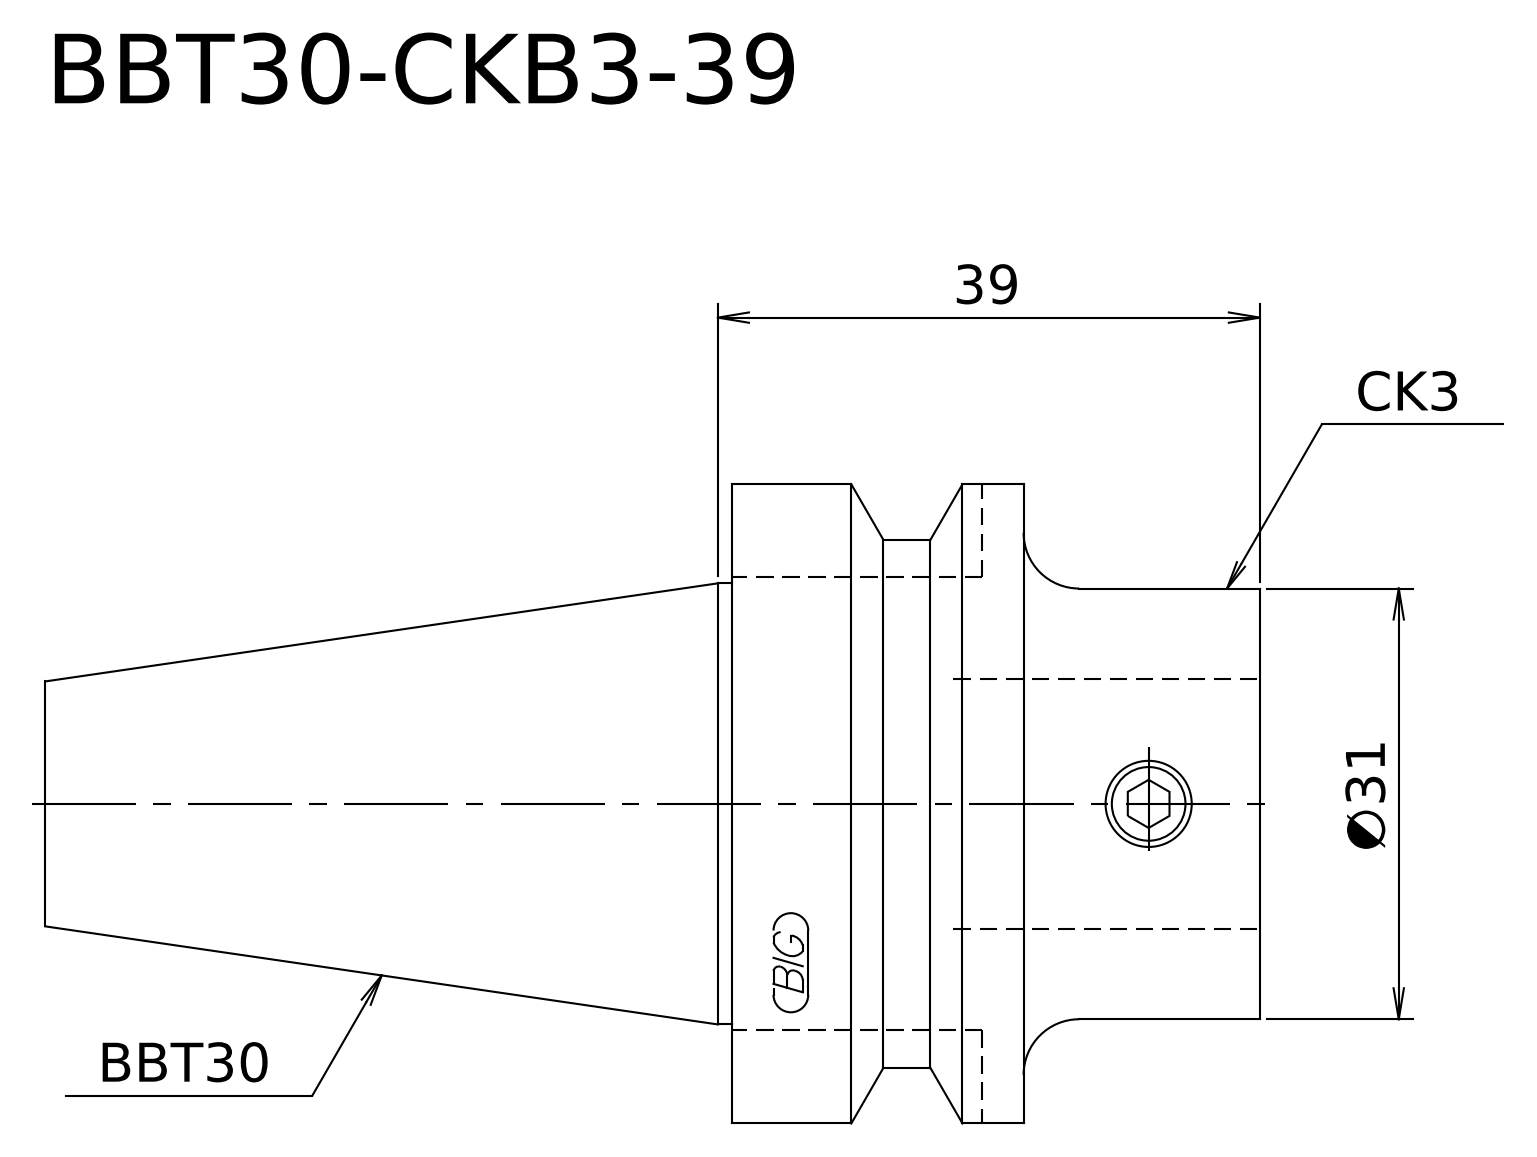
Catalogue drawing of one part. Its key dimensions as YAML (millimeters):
step_written_by: "Kubotek KeyCreator V8.5.1 (14335) (CONFIG_CONTROL_DESIGN)"
units: millimeters
bodies: {solids: 1, faces: 13, planar: 4, cylindrical: 5, other: 4}
overall_size: [87.4, 46, 46]
volume: 70636
surface_area: 11574
round_bosses_or_shafts:
  - {diameter: 46, count: 1}
  - {diameter: 38, count: 1}
  - {diameter: 31.75, count: 1}
  - {diameter: 31, count: 1}
face_to_face_distances: [38, 17, 21, 87.4, 70.4, 49.4]
